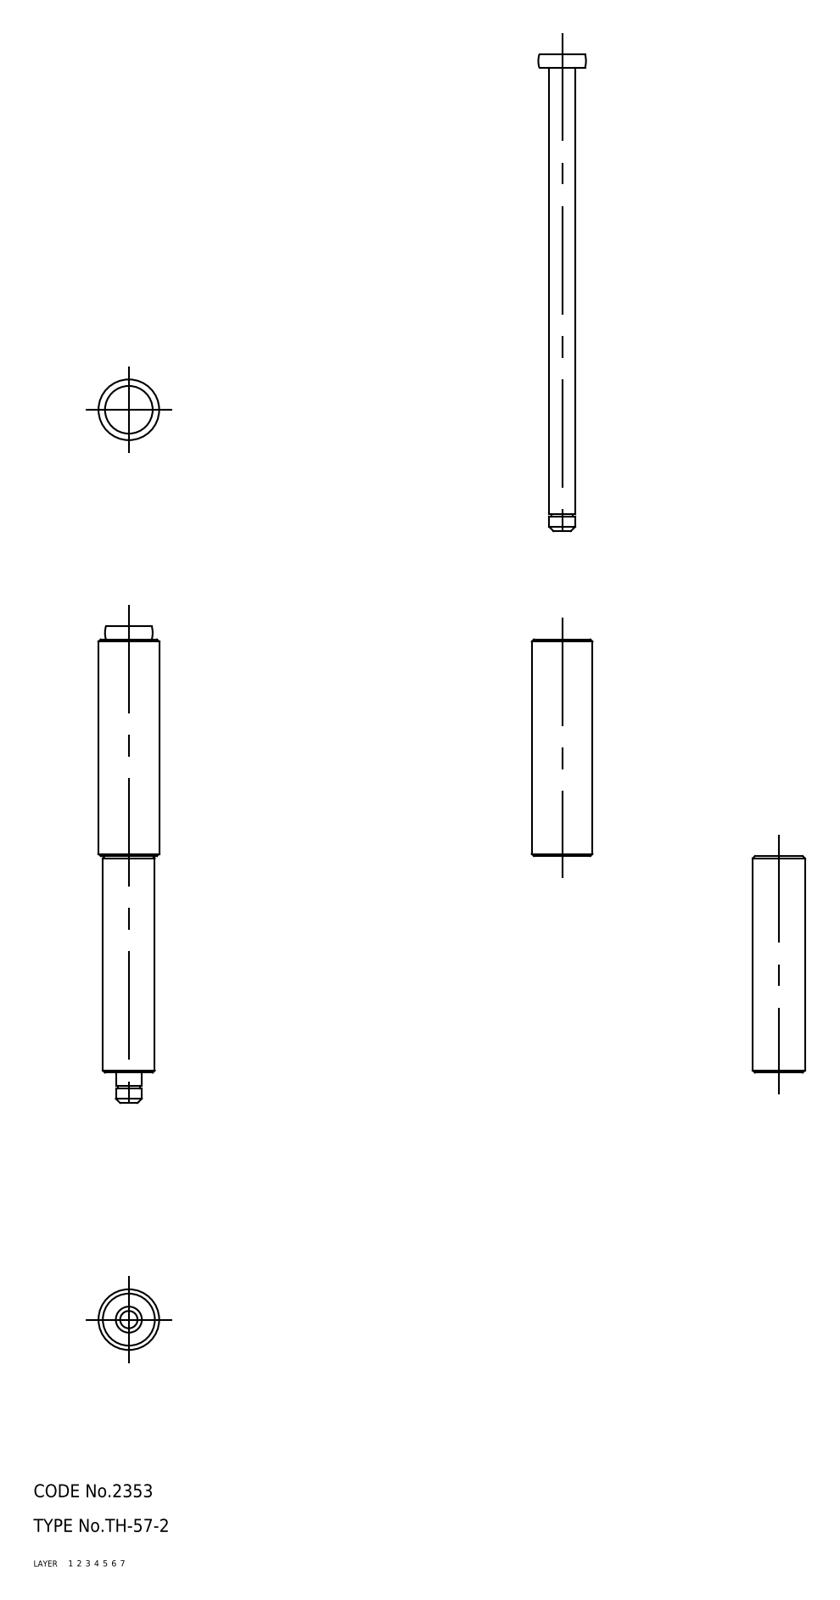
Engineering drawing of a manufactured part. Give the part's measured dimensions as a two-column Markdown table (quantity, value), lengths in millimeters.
| quantity | value |
| --- | --- |
| part name | shaft; collar_B; collar_A; TH_57_2_11629_36 |
| STEP written by | CADfix (AUTOMOTIVE_DESIGN) |
| units | millimeters |
| bodies | 3 solids, 34 faces (0 planar, 0 cylindrical, 34 other) |
| overall size | 110 × 14 × 14 |
| volume | 13 819 mm³ |
| surface area | 8 646 mm² |
